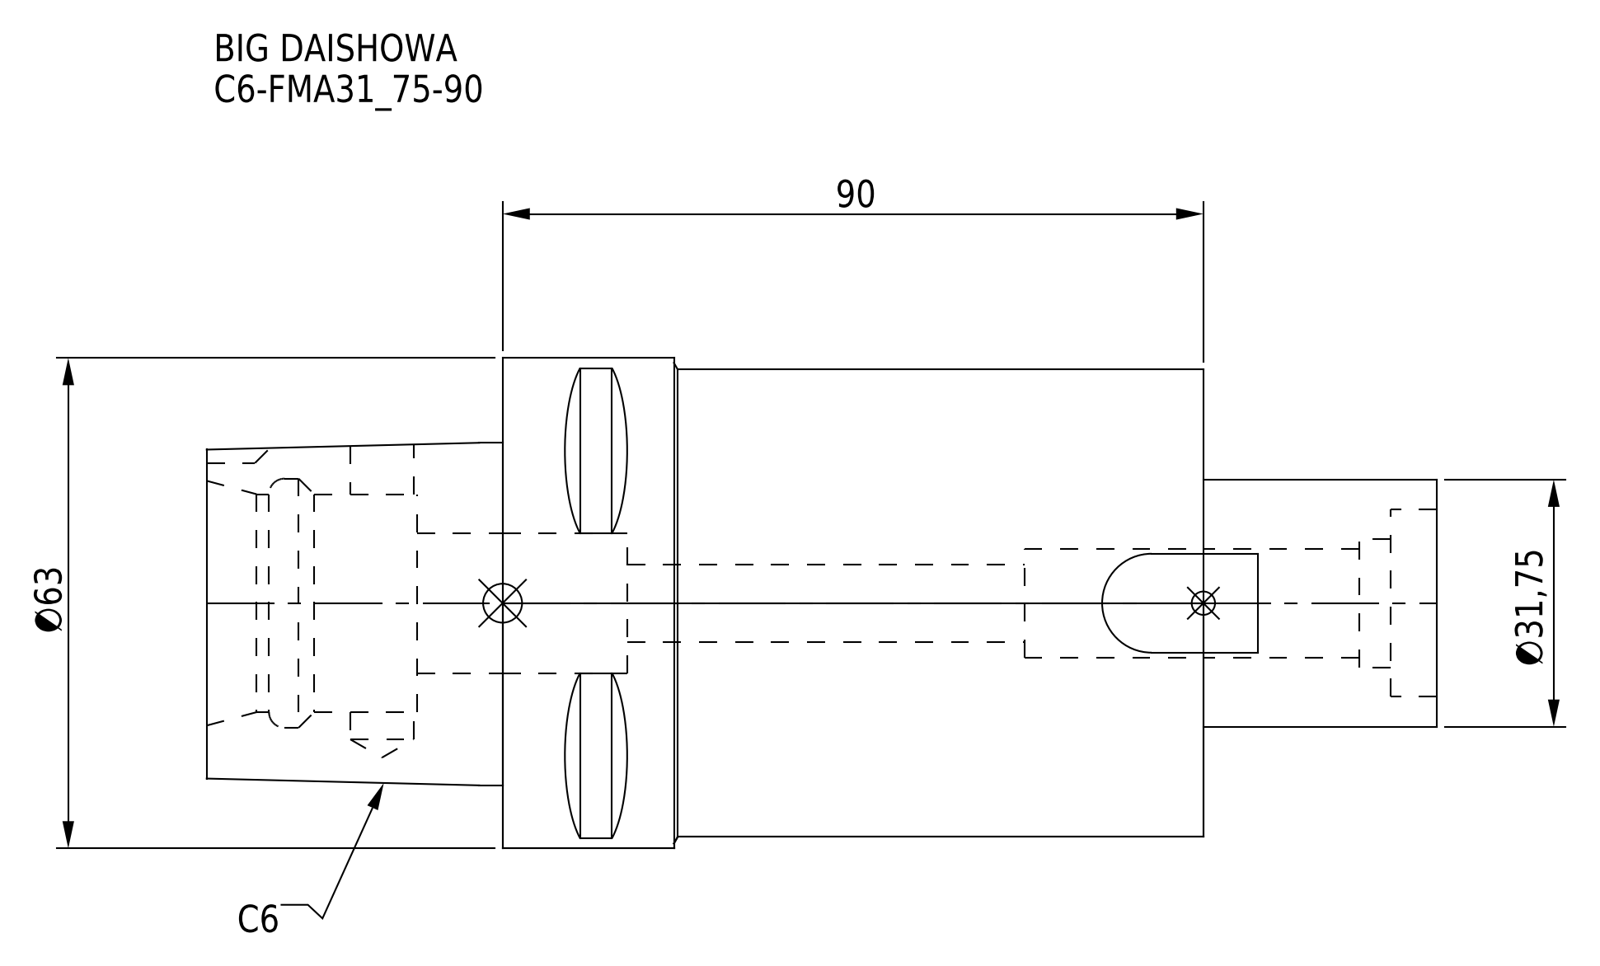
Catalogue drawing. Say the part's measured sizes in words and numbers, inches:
The part is named "C6-FMA31_75-90". Its 3-D file was written by "CREO PARAMETRIC BY PTC INC, 2016380 (AUTOMOTIVE_DESIGN)". It is 1 solid with 81 faces: 42 planar, 27 cylindrical and 12 other. Overall it measures 6.22 by 2.48 by 2.48 inches. Its volume is 18.33 cubic inches and its surface area 62.85 square inches. Round holes: 1 of diameter 0.319, 1 of diameter 0.394, 1 of diameter 0.551, 1 of diameter 0.65, 1 of diameter 0.709, 1 of diameter 0.945, 1 of diameter 1.102, 1 of diameter 1.26. Round bosses or shafts: 1 of diameter 2.48, 1 of diameter 2.362, 1 of diameter 1.25. Partial cylindrical surfaces (rounded edges, fillets, slot ends): 1 of radius 0.197. The main face-to-face distances are 3.543, 0.433, 1.063, 5.039, 1.496, 1.181, 0.236, 3.976, 0.906, 4.724.
